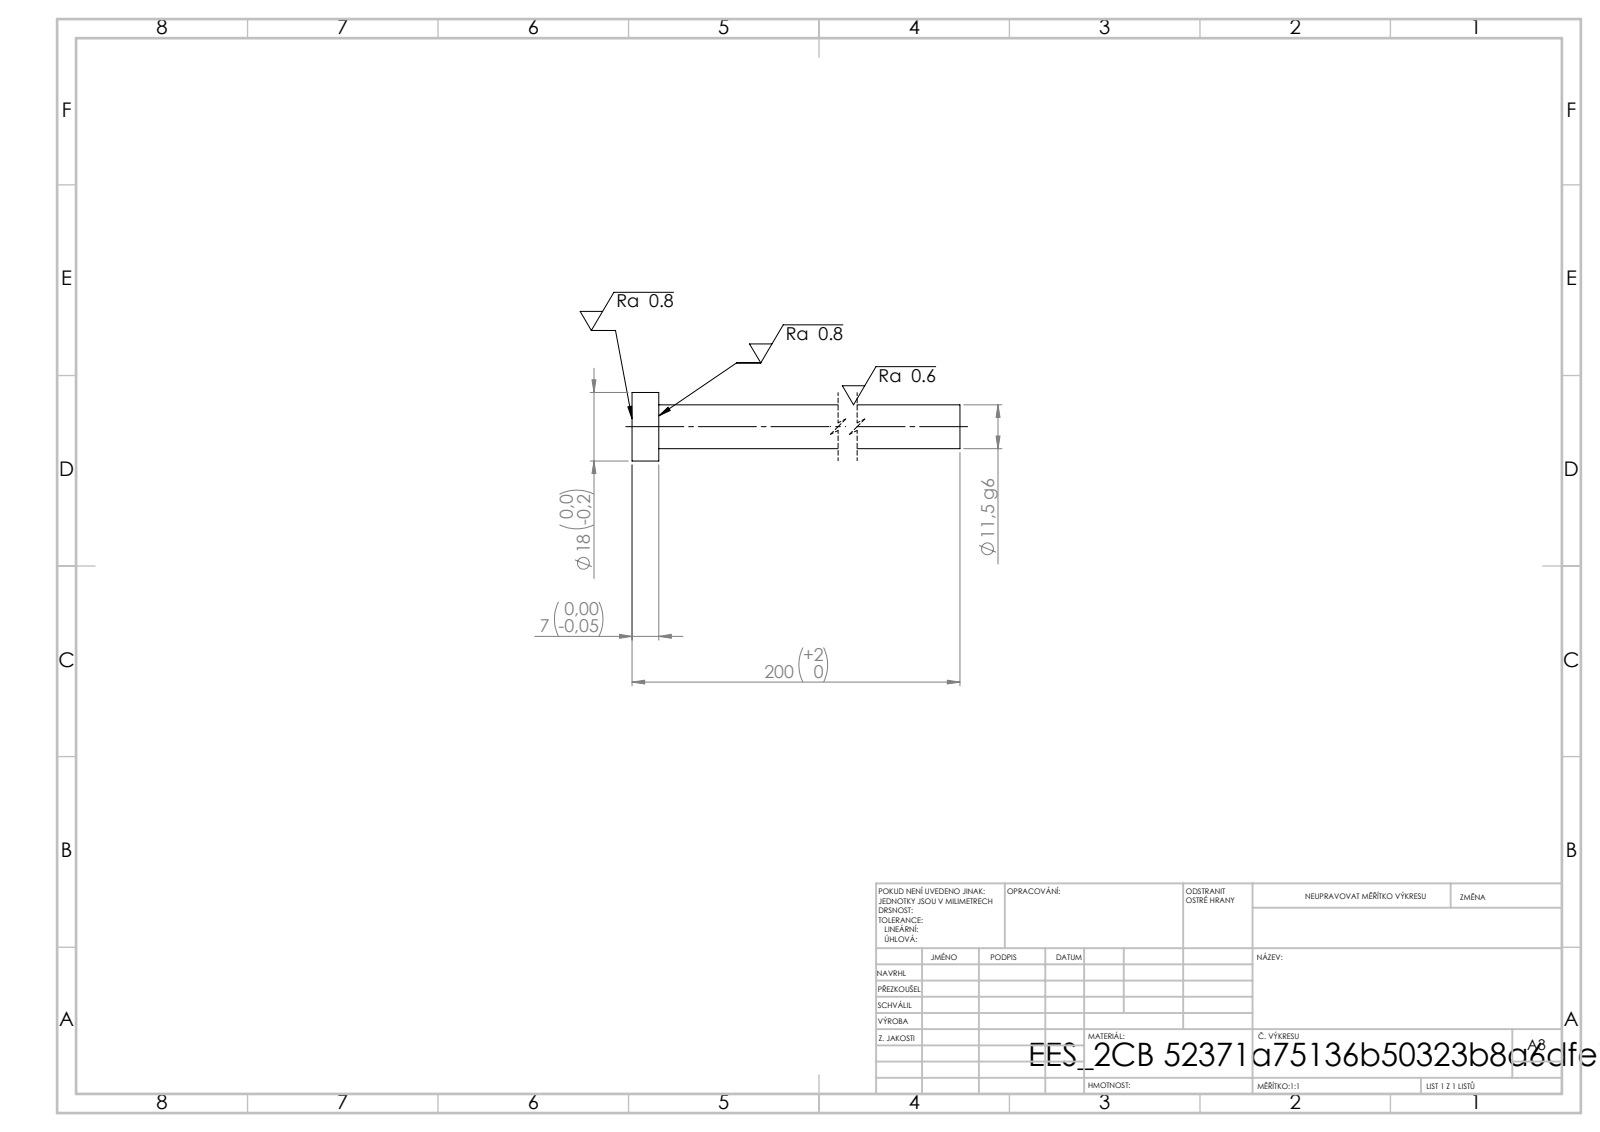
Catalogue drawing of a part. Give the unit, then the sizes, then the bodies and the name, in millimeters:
Units: millimetres
Overall size (bounding box): 200 × 18 × 18
Round bosses / shafts (diameter × count): ⌀18 ×1, ⌀11.5 ×1
Main face-to-face distances: 7, 200, 193
Volume: 21 828 mm³ · Surface area: 7 878 mm²
Bodies: 1 solid, 7 faces (3 planar, 4 cylindrical, 0 other)
STEP written by: SolidWorks 2019 (CONFIG_CONTROL_DESIGN)
